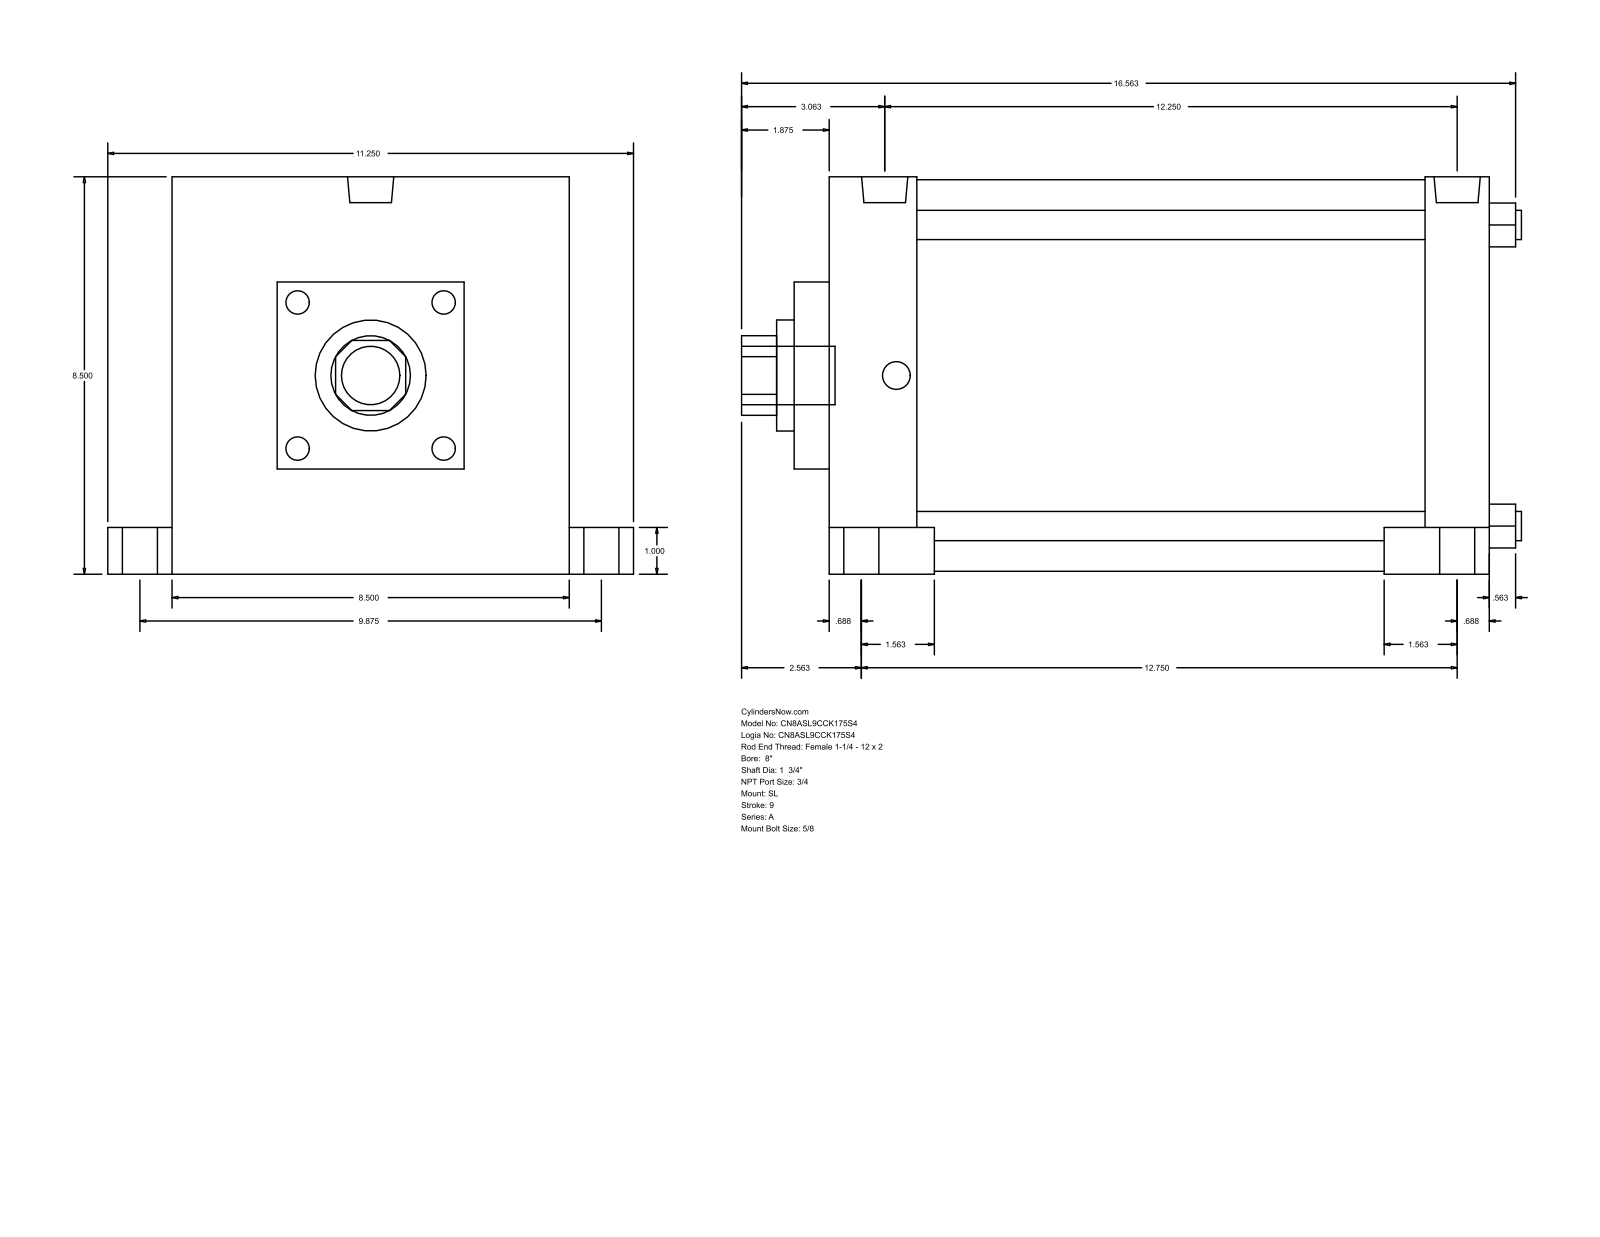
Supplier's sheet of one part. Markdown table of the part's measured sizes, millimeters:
| quantity | value |
| --- | --- |
| part name | A_SL__0800_1.75 |
| STEP written by | GSSL Pune (CONFIG_CONTROL_DESIGN) |
| units | millimeters |
| bodies | 0 solids, 117 faces (85 planar, 32 cylindrical, 0 other) |
| overall size | 423.86 × 285.75 × 215.9 |
| round holes (diameter × count) | 15.88 × 4, 44.45 × 1, 60.33 × 1, 212.72 × 1 |
| round bosses / shafts (diameter × count) | 25.4 × 4, 19.05 × 4, 15.08 × 4, 25.12 × 2, 31.75 × 1 |
| partial cylindrical surfaces (radius × count) | 21.63 × 1 |
| main face-to-face distances | 358.78, 215.9, 34.92, 47.63, 311.15, 323.86, 276.23, 57.15, 19.05, 158.75 |
| hole center spacings | 115.67, 163.58, 231.34 |
